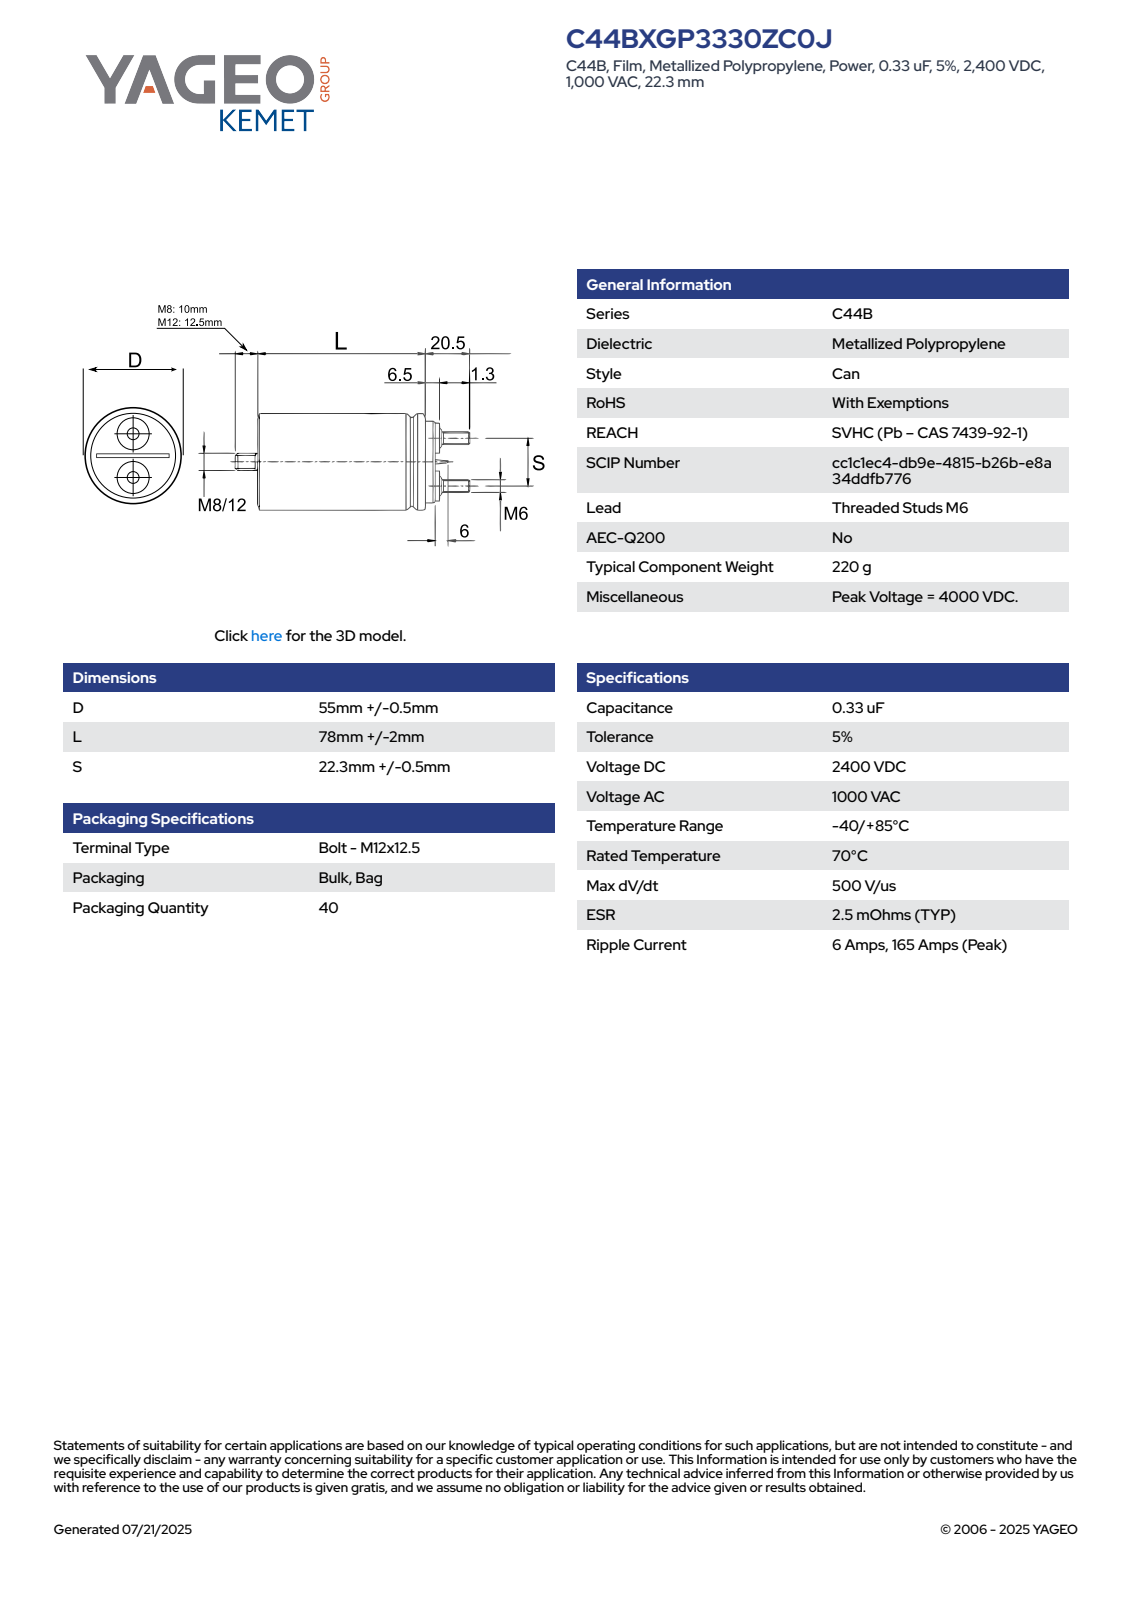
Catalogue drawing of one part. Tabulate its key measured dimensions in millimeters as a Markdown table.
| quantity | value |
| --- | --- |
| part name | CFP_M6_55X78_D55.5L80S22.8 |
| STEP written by | SolidWorks 2014 (AUTOMOTIVE_DESIGN) |
| units | millimeters |
| bodies | 1 solid, 117 faces (35 planar, 39 cylindrical, 43 other) |
| overall size | 112.5 × 55.51 × 55.5 |
| volume | 200 311 mm³ |
| surface area | 21 670 mm² |
| round bosses / shafts (diameter × count) | 15.25 × 2, 11.01 × 2, 6 × 2, 55.5 × 1, 49.12 × 1, 12 × 1 |
| partial cylindrical surfaces (radius × count) | 0.35 × 1, 27.76 × 1 |
| main face-to-face distances | 84, 80, 4, 0.7, 86.5, 6.5, 2.5, 87.5, 7.5, 3.5 |
